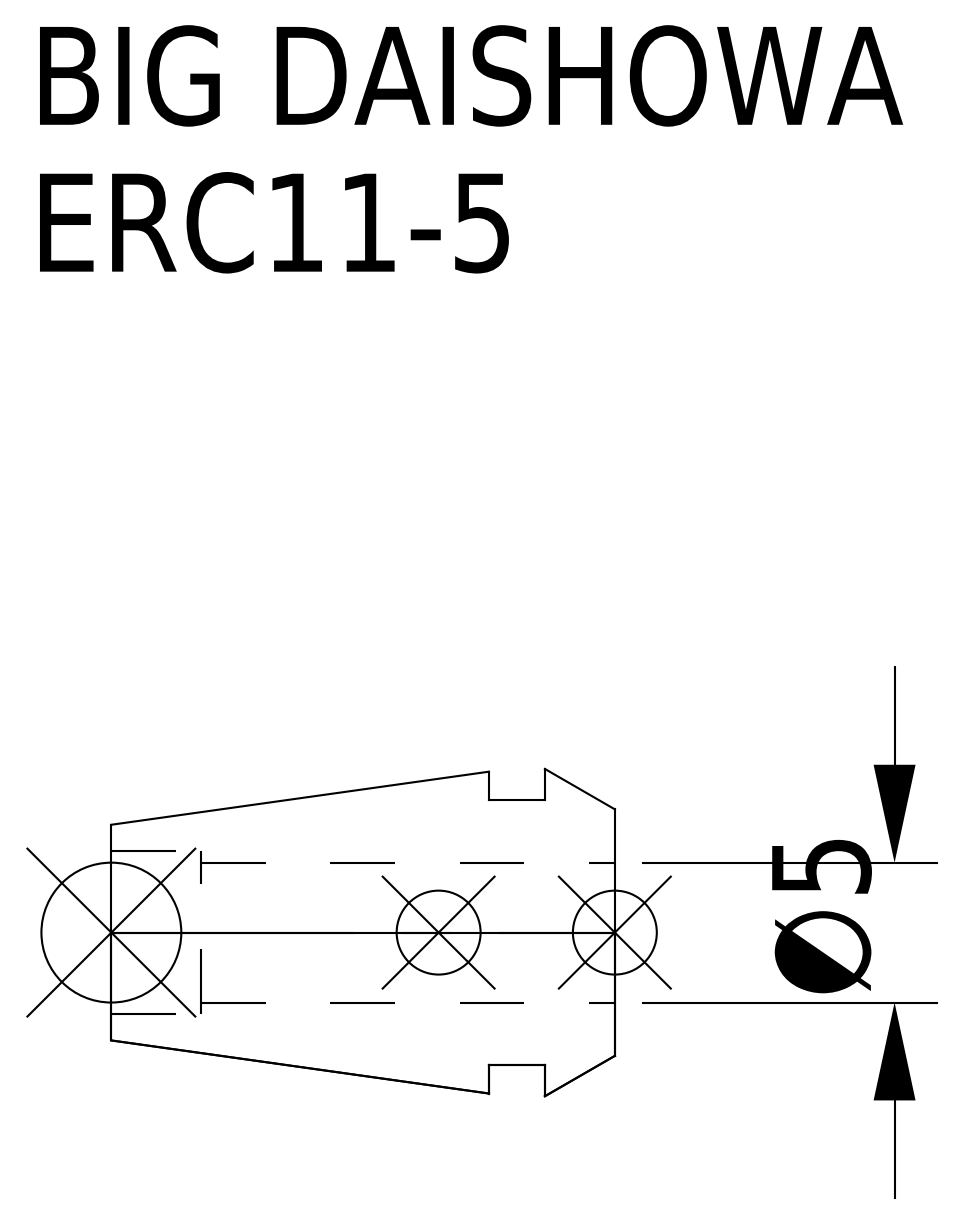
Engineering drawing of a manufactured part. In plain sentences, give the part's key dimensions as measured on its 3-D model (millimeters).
The part is named "ERC11-5". Its 3-D file was written by "CREO PARAMETRIC BY PTC INC, 2016380 (AUTOMOTIVE_DESIGN)". It is 1 solid with 15 faces: 5 planar, 6 cylindrical and 4 other. Overall it measures 18 by 11.7 by 11.7 millimeters. Its volume is 966 cubic millimeters and its surface area 993 square millimeters. Round holes: 1 of diameter 5, 1 of diameter 5.8. Round bosses or shafts: 1 of diameter 9.5. The main face-to-face distances are 2.5, 4.5, 2, 18, 15.5, 13.5, 14.79, 12.29, 10.29, 3.21.
